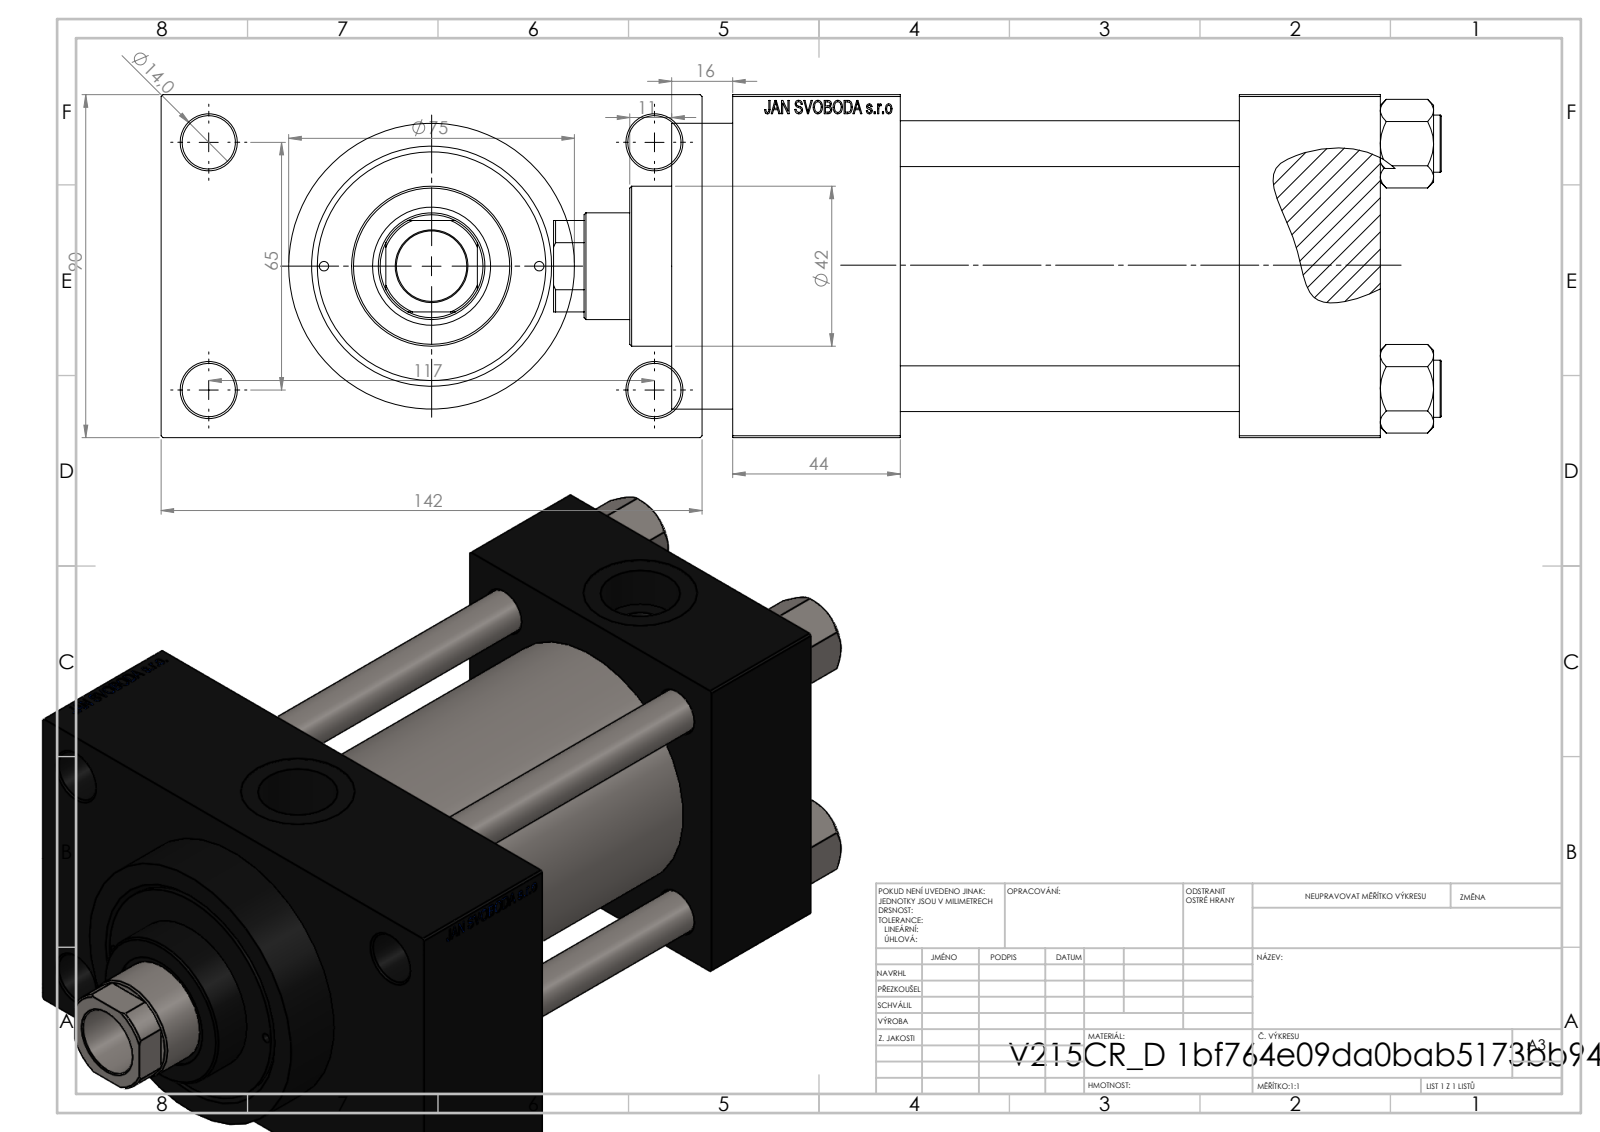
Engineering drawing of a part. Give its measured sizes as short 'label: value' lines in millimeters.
name: V215_VC_A; V215CR_D_Body; NUT_M5_D; V215CR_VCP_D (+1 more)
written by: SolidWorks 2019 (CONFIG_CONTROL_DESIGN)
unit: mm
bodies: 11 solids, 1112 faces (499 planar, 93 cylindrical, 520 other)
size: 233 × 142 × 90
volume: 1 156 000 mm³; area: 218 126 mm²
holes: 4× ⌀12, 4× ⌀14, 2× ⌀2.5, 2× ⌀7, 2× ⌀20.96, 2× ⌀30, 1× ⌀18.5, 1× ⌀28, 1× ⌀31, 1× ⌀50, 1× ⌀60, 1× ⌀63
bosses: 4× ⌀15, 1× ⌀75, 1× ⌀69, 1× ⌀42
rounds: 1× R13.5
face distances: 90, 89, 37, 126, 133, 170, 44, 26, 116, 142
hole spacings: 26.35, 32.39, 44.4, 45.47, 64.3, 66.92, 68.42, 69.81
